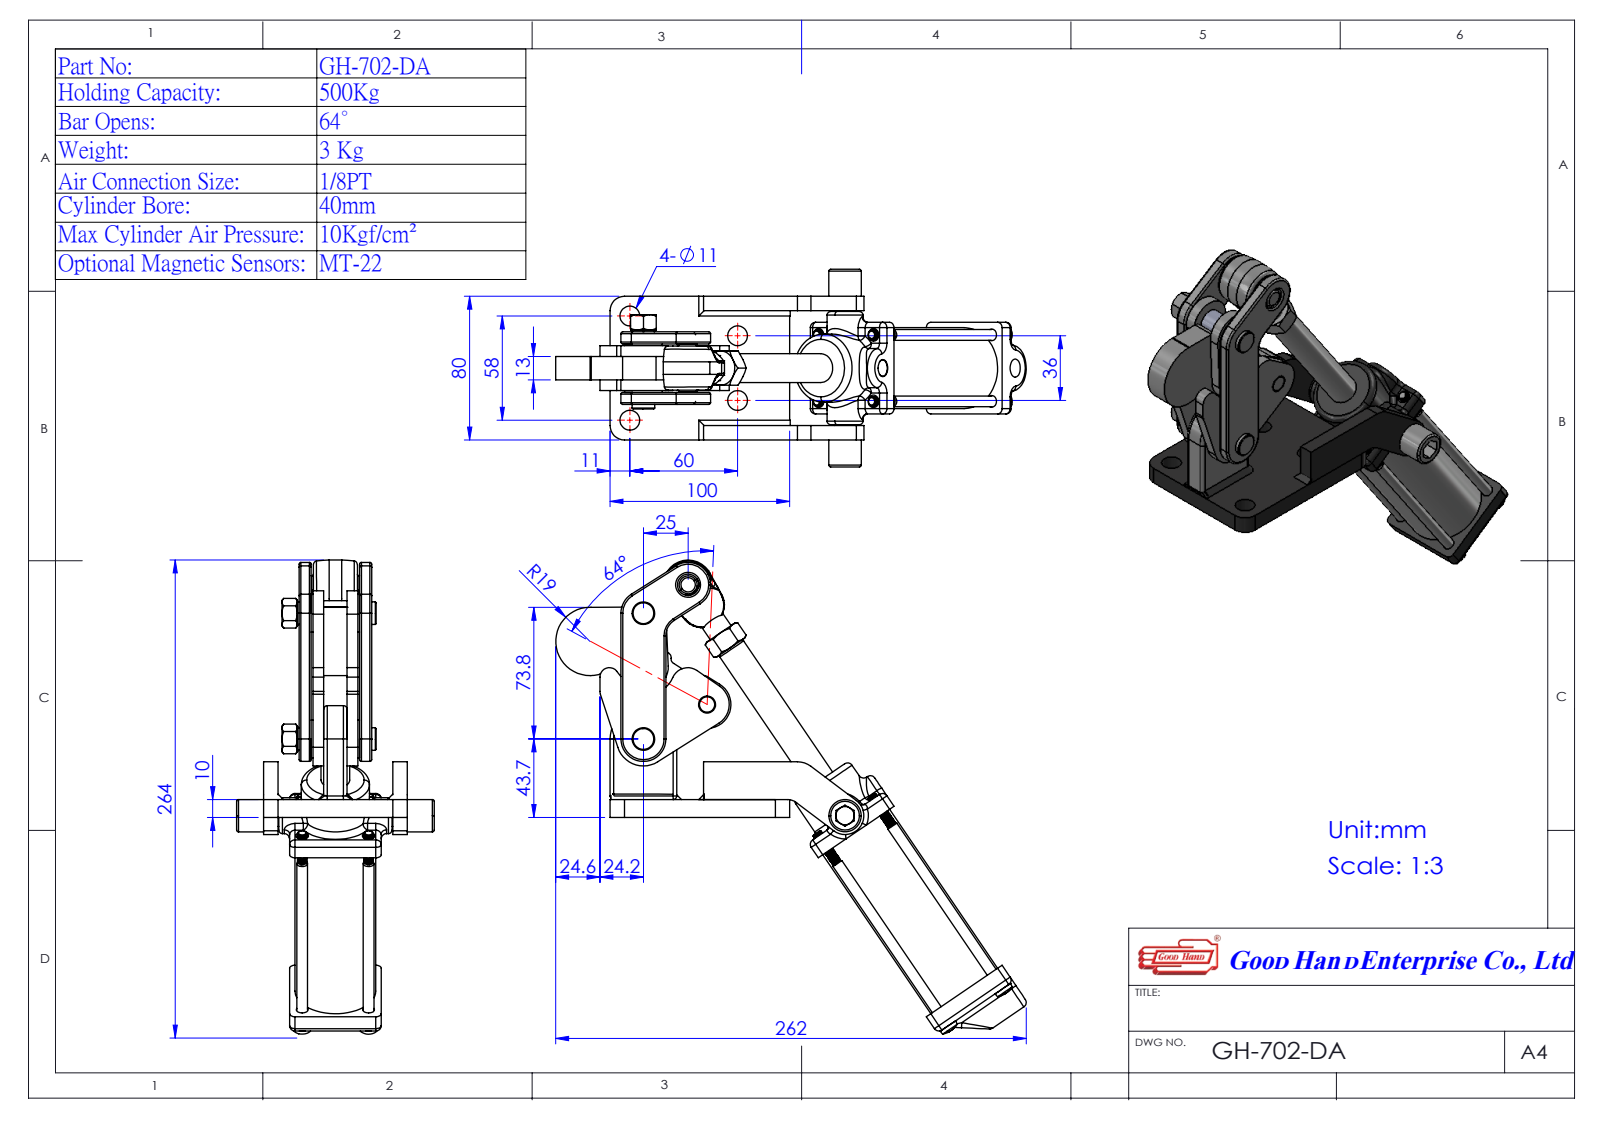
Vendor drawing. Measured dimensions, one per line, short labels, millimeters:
name: Group7^GH-702-DA(簡化); 702D-PISTON-1^GH-702-DA(簡化); 702DA氣壓缸-1^GH-702-DA(簡化); 3700208-1^GH-702-DA(簡化) (+4 more)
written by: SolidWorks 2016 (AUTOMOTIVE_DESIGN)
unit: mm
bodies: 7 solids, 861 faces (273 planar, 214 cylindrical, 374 other)
size: 263.78 × 262.53 × 110
volume: 589 517 mm³; area: 153 269 mm²
holes: 4× ⌀8, 4× ⌀11, 2× ⌀7.9, 2× ⌀10, 2× ⌀16, 1× ⌀6.8, 1× ⌀9.55, 1× ⌀10.2, 1× ⌀12
bosses: 4× ⌀6, 2× ⌀21, 2× ⌀14, 2× ⌀12.6, 2× ⌀9.52, 1× ⌀45, 1× ⌀40, 1× ⌀38
rounds: 27× R3, 6× R12.5, 5× R8, 4× R2, 4× R5.15, 3× R5, 2× R10, 2× R15
face distances: 19, 6, 13, 25, 10, 7.7, 13.7, 26.7, 32.7, 19.8
hole spacings: 61, 76.22, 29.49, 30, 36, 39.97, 51.47, 58
